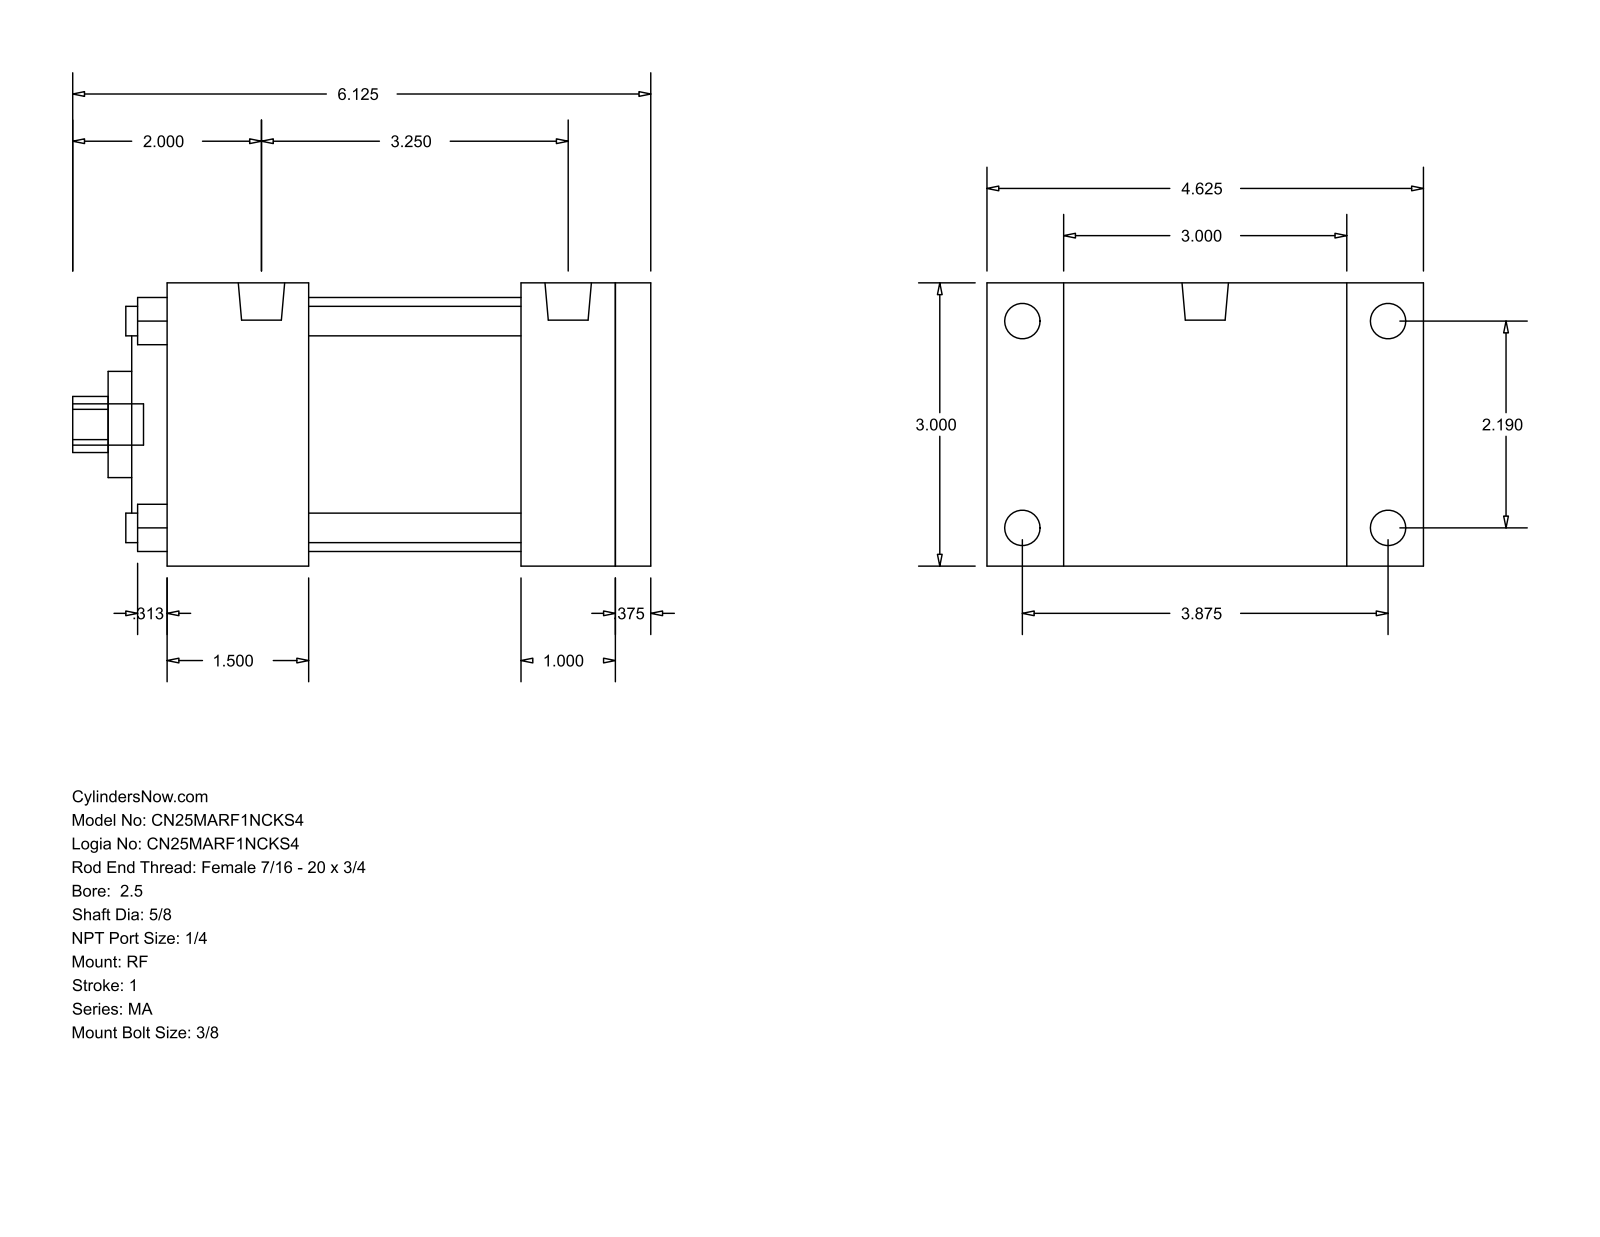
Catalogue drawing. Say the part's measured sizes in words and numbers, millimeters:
The part is named "MA_RF__0250_0.625". Its 3-D file was written by "GSSL Pune (CONFIG_CONTROL_DESIGN)". It is 0 solids with 94 faces: 65 planar, 29 cylindrical and 0 other. Overall it measures 155.57 by 117.47 by 76.2 millimeters. Round holes: 4 of diameter 7.94, 1 of diameter 15.88, 1 of diameter 28.57, 1 of diameter 50.8, 1 of diameter 68.33. Round bosses or shafts: 4 of diameter 9.53, 4 of diameter 7.94, 2 of diameter 12.49, 1 of diameter 11.11. Partial cylindrical surfaces (rounded edges, fillets, slot ends): 1 of radius 7.54. The main face-to-face distances are 76.2, 130.17, 9.52, 120.65, 25.4, 57.15, 38.1, 95.25, 82.55, 92.07. The hole center spacings are 39.33, 55.62, 78.66.
